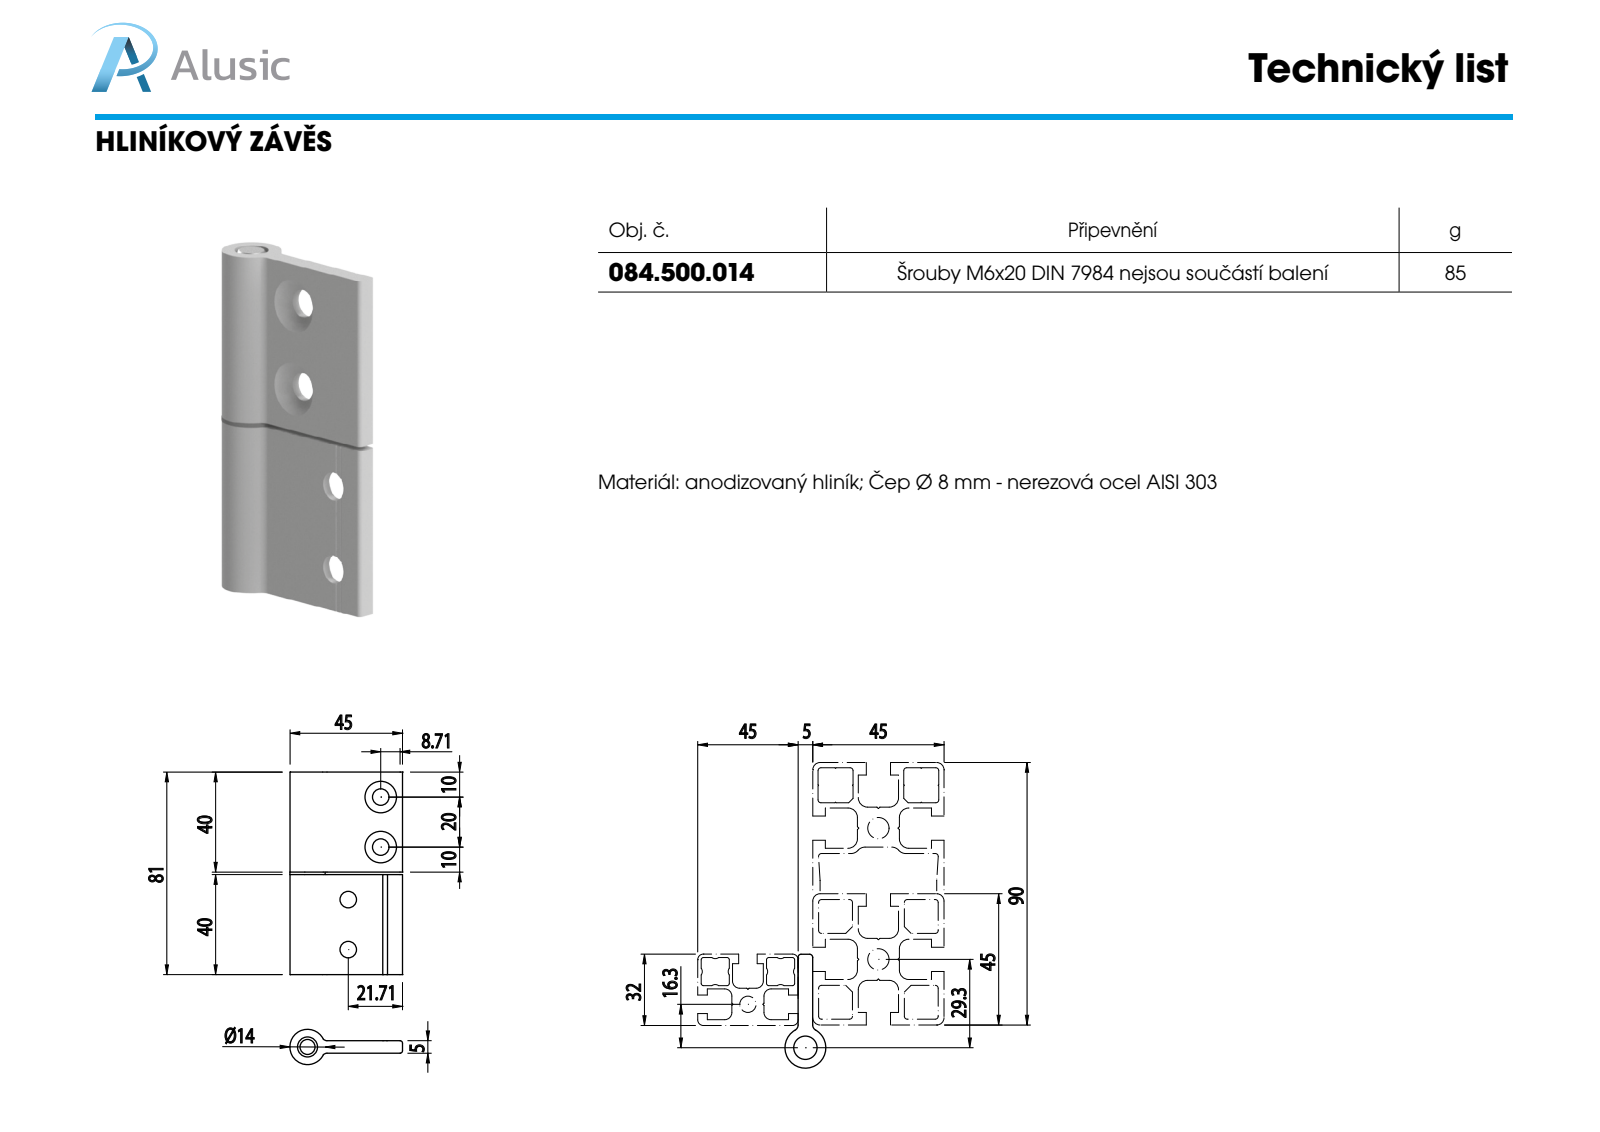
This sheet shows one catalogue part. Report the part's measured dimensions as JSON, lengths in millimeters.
{"part_name": "084.500.010L; 084.500.014; 084.500.001.C; PERNO CERNIERA_084.500.001.B (+1 more)", "step_written_by": "SolidWorks 2011 (CONFIG_CONTROL_DESIGN)", "units": "millimeters", "bodies": {"solids": 4, "faces": 196, "planar": 148, "cylindrical": 36, "other": 12}, "overall_size": [81, 45.05, 14.1], "volume_mm3": 23727, "surface_area_mm2": 13972, "round_holes": [[6.6, 4], [8, 1], [8.1, 1]], "round_bosses_or_shafts": [[14.1, 1], [14, 1]], "partial_cylinders_radius": [[0.2, 2], [1, 2], [2, 2]], "face_to_face_distances": [5, 40, 41, 1, 81, 6.11, 6.12, 3.26, 34.5, 5.5], "hole_center_spacings": [20, 43.01, 24.7, 62.37]}
